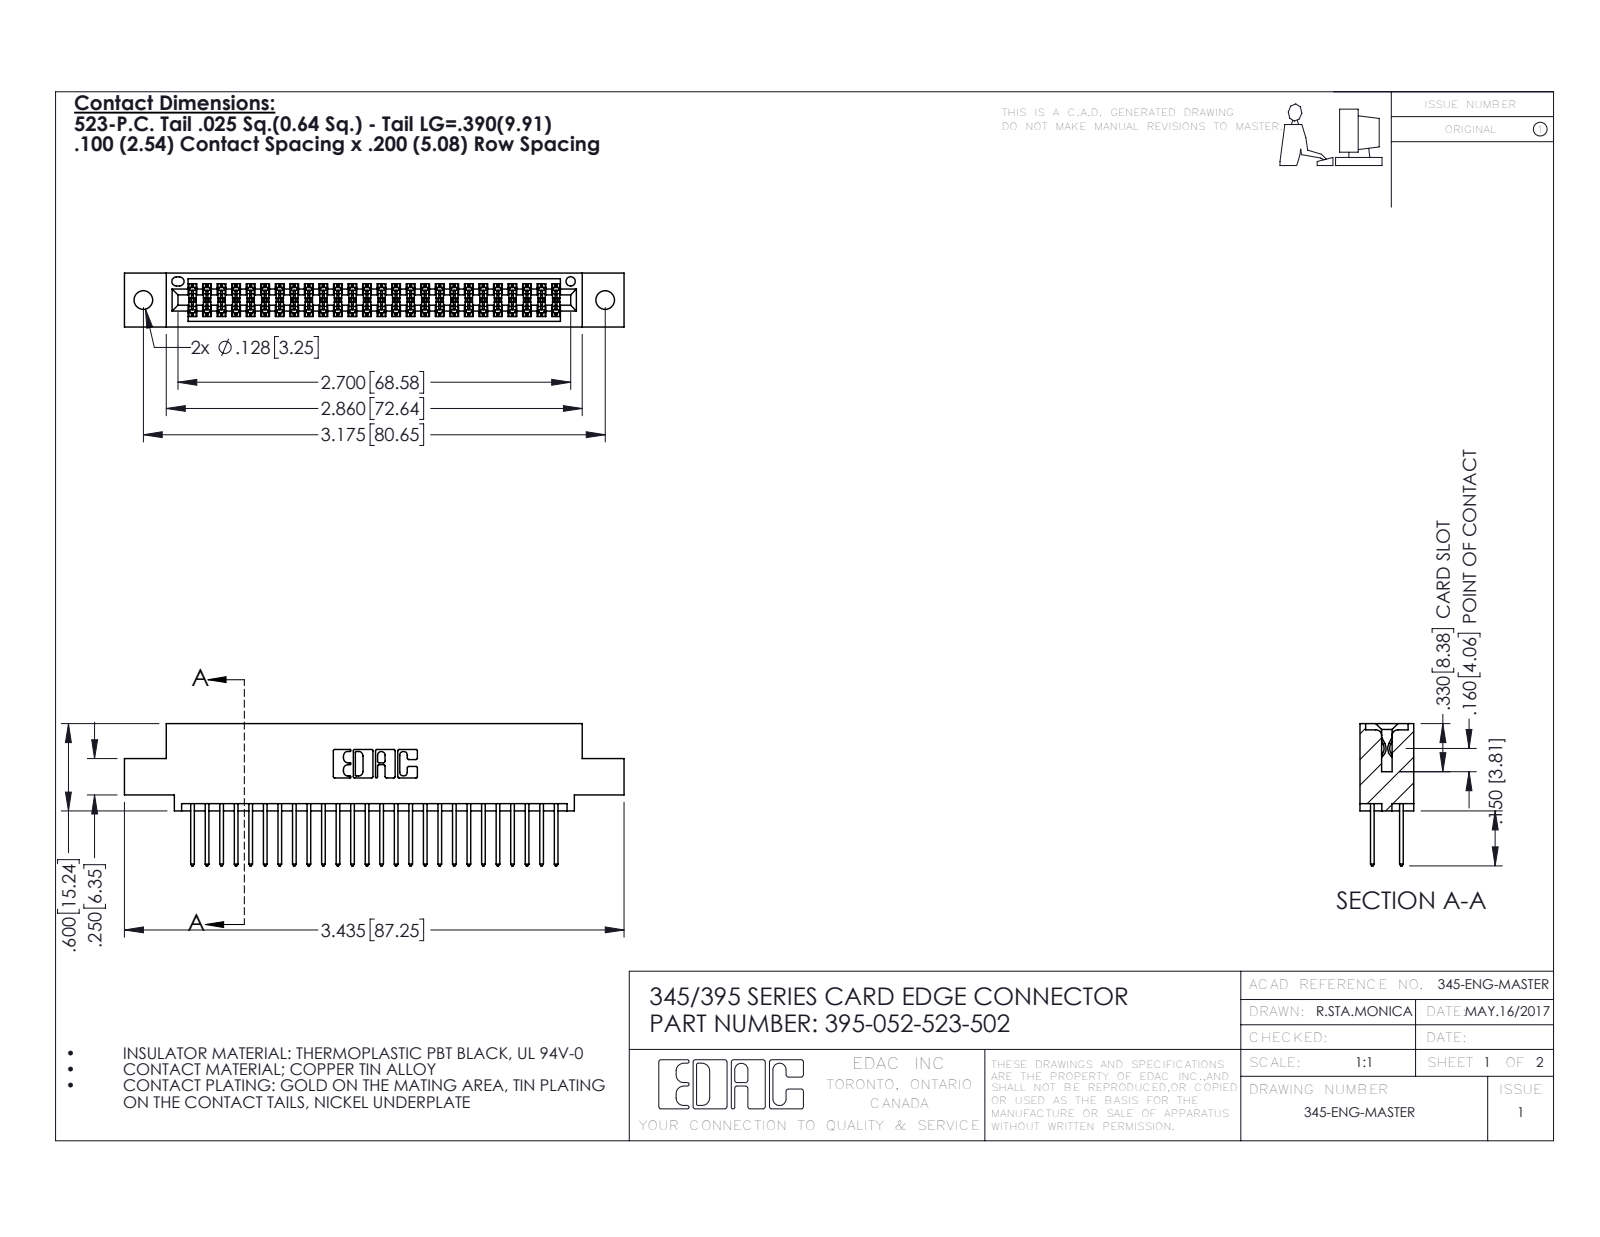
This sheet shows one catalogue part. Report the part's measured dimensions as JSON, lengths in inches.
{"part_name": "345-292-001_345-293-123; 345 Part_0.110 Offset - 0.128 Dia; 395-052-523-502", "step_written_by": "SolidWorks 2016 (CONFIG_CONTROL_DESIGN)", "units": "inches", "bodies": {"solids": 53, "faces": 2730, "planar": 1800, "cylindrical": 930, "other": 0}, "overall_size": [3.435, 0.977, 0.37], "volume_in3": 0.508, "surface_area_in2": 19.05, "round_holes": [[0.128, 2], [0.064, 1]], "partial_cylinders_radius": [[0.006, 78], [0.01, 52], [0.01, 22], [0.007, 6], [0.031, 6], [0.026, 3], [0.014, 2], [0.019, 2]], "face_to_face_distances": [0.298, 0.072, 0.2, 0.098, 0.272, 0.025, 0.37, 0.225, 0.175, 0.149], "hole_center_spacings": [0.27, 2.94, 3.175]}
